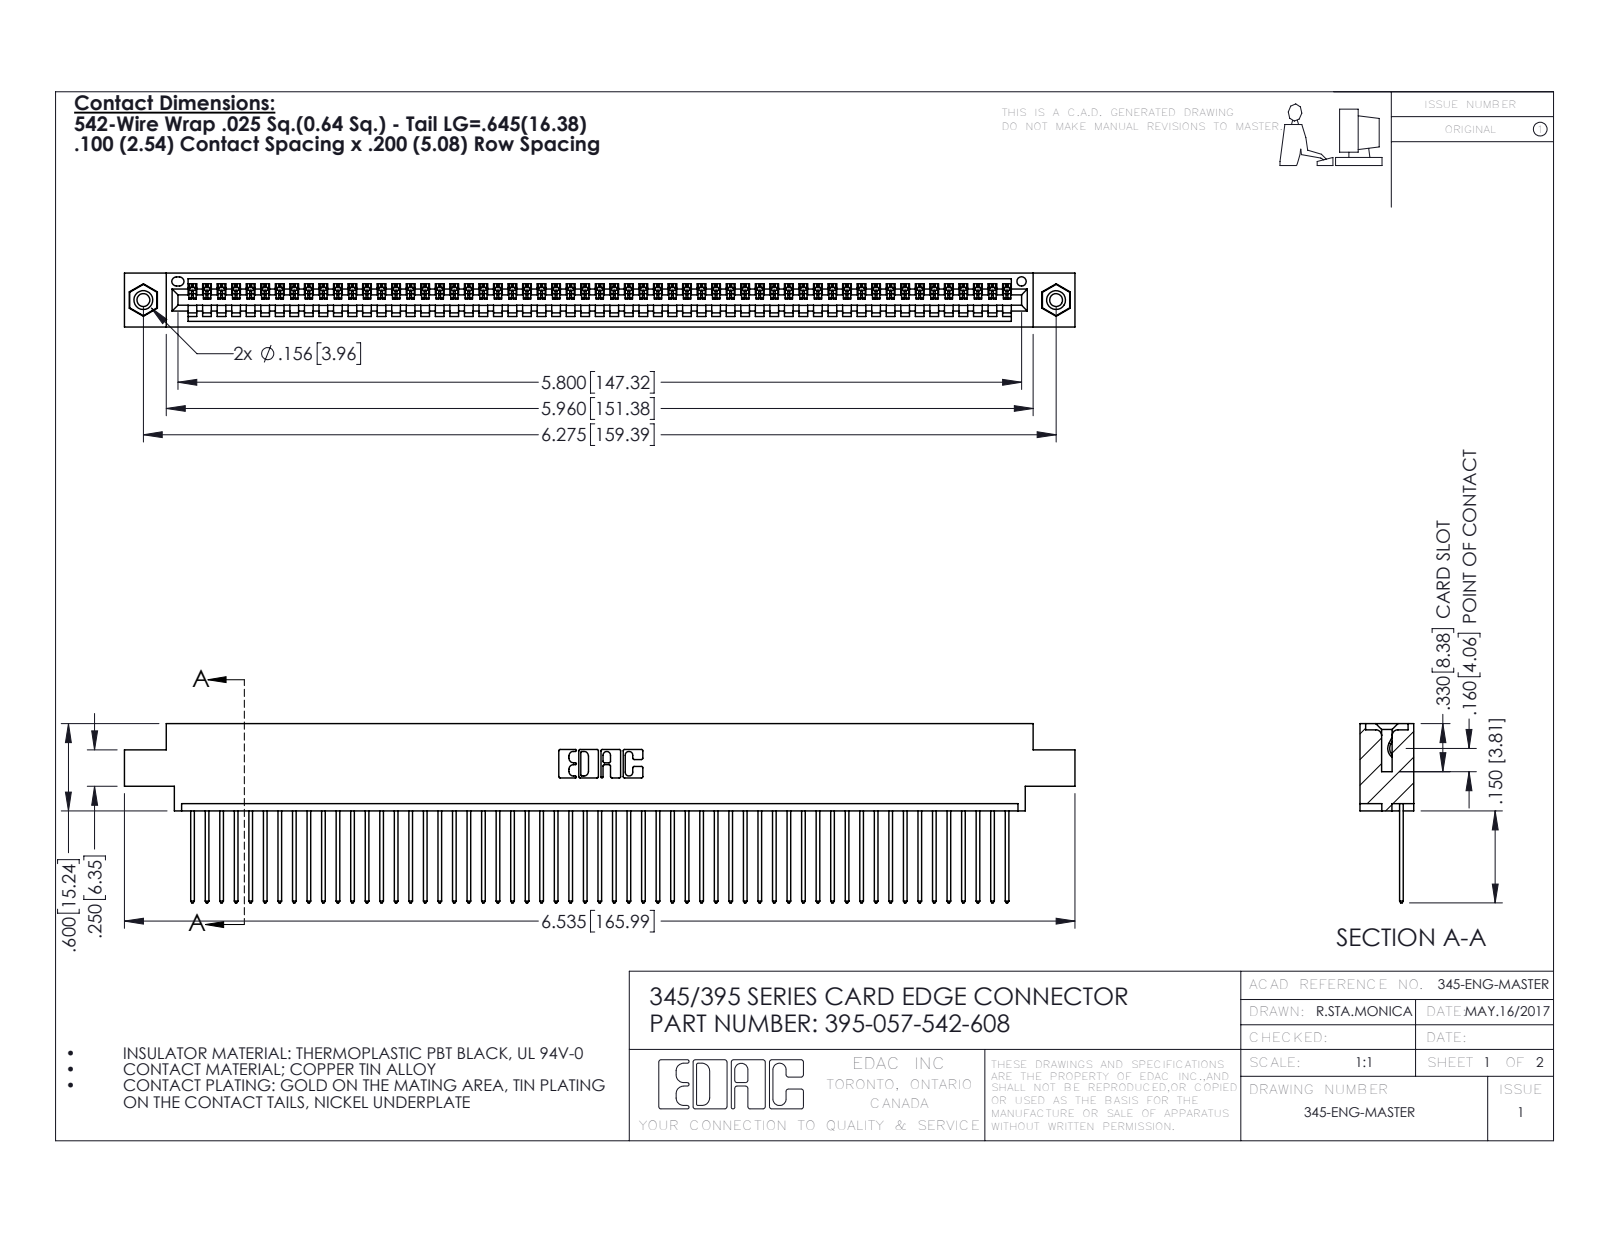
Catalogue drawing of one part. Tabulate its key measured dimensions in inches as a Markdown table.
| quantity | value |
| --- | --- |
| part name | 345-292-001_345-293-142; 395-057-542-608; 345-250-001_345-250-003-102; 345 Part_0.170 Offset - 0.156 Dia-TI |
| STEP written by | SolidWorks 2016 (CONFIG_CONTROL_DESIGN) |
| units | inches |
| bodies | 60 solids, 3496 faces (2396 planar, 1084 cylindrical, 16 other) |
| overall size | 6.535 × 1.232 × 0.37 |
| volume | 0.97 in³ |
| surface area | 34.53 in² |
| round holes (diameter × count) | 0.089 × 2, 0.125 × 2, 0.156 × 2, 0.064 × 1 |
| round bosses / shafts (diameter × count) | 0.155 × 2 |
| partial cylindrical surfaces (radius × count) | 0.006 × 114, 0.01 × 114, 0.01 × 22, 0.007 × 6, 0.031 × 6, 0.026 × 3, 0.031 × 2, 0.04 × 2 |
| main face-to-face distances | 0.072, 0.298, 0.37, 0.098, 0.272, 0.025, 0.2, 0.225, 0.175, 0.149 |
| hole center spacings | 0.27, 6.039, 6.275 |
